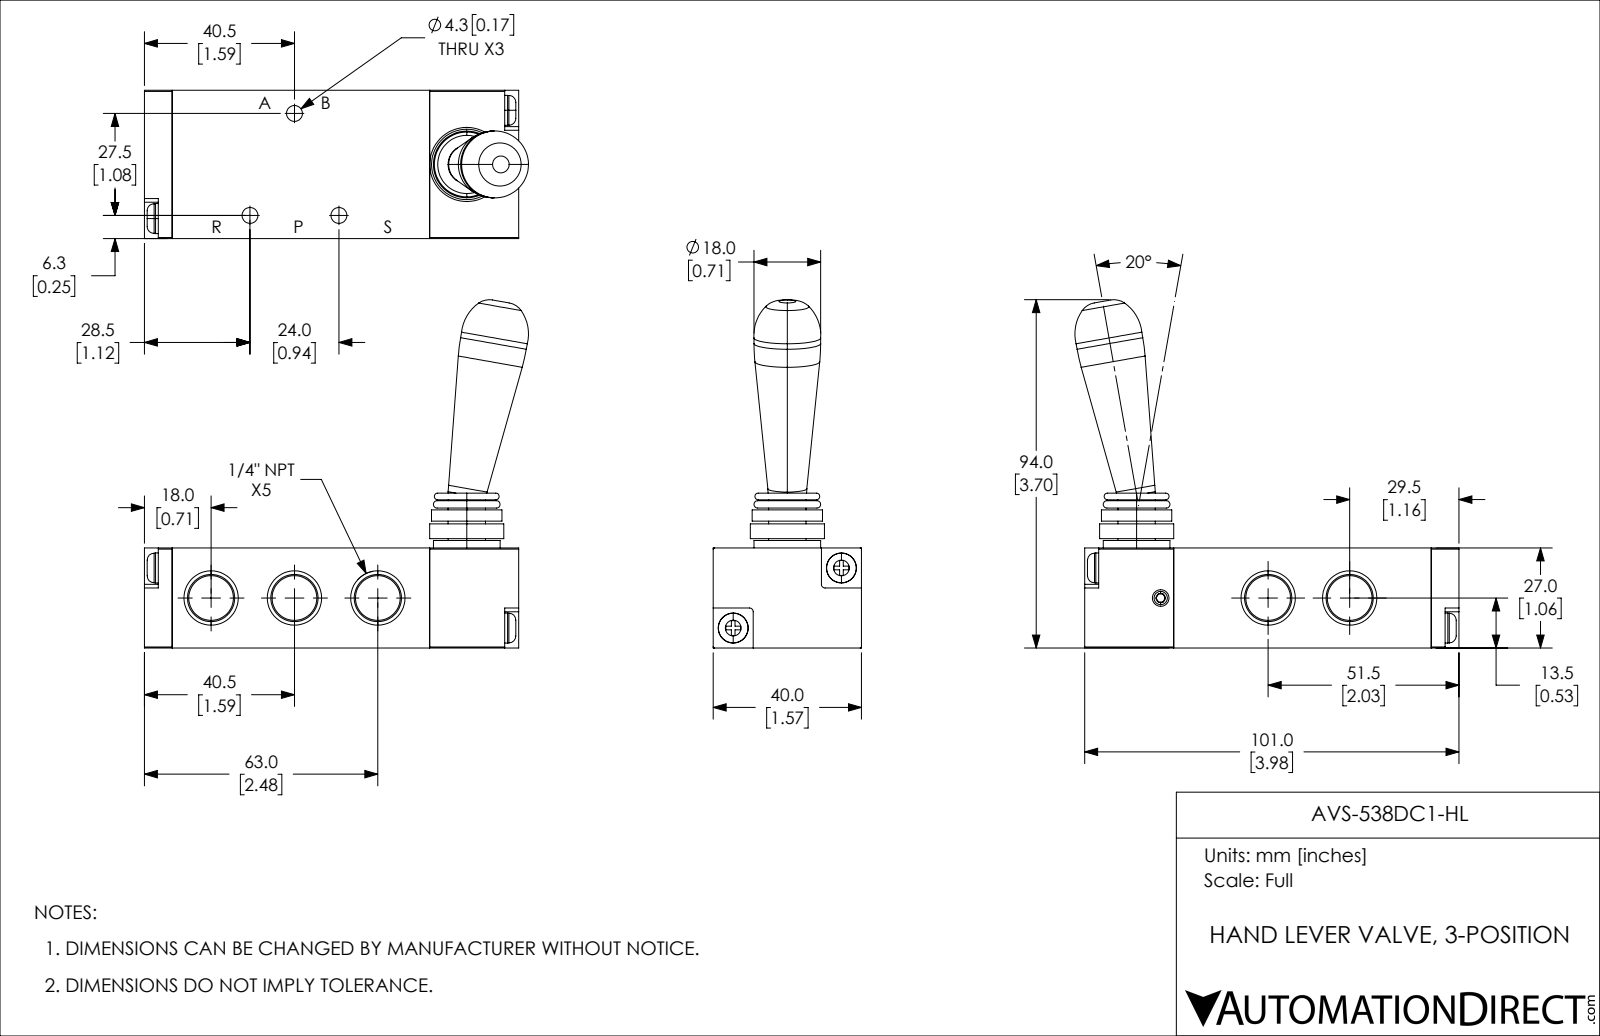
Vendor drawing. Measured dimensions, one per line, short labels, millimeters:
name: AVS-538DC1-HL
written by: SolidWorks 2018 (AUTOMOTIVE_DESIGN)
unit: mm
bodies: 4 solids, 219 faces (118 planar, 57 cylindrical, 44 other)
size: 103.66 × 93.95 × 40
volume: 111 706 mm³; area: 29 053 mm²
holes: 3× ⌀4.3, 1× ⌀4.5, 1× ⌀18
bosses: 4× ⌀8.1, 4× ⌀8, 1× ⌀20, 1× ⌀19, 1× ⌀18, 1× ⌀10.1, 1× ⌀3.6
rounds: 4× R0.3, 4× R1
face distances: 27, 40, 69.5, 93.5, 24, 101, 77, 7.5, 2, 4
hole spacings: 30, 24, 37.14, 48.49, 60.09
